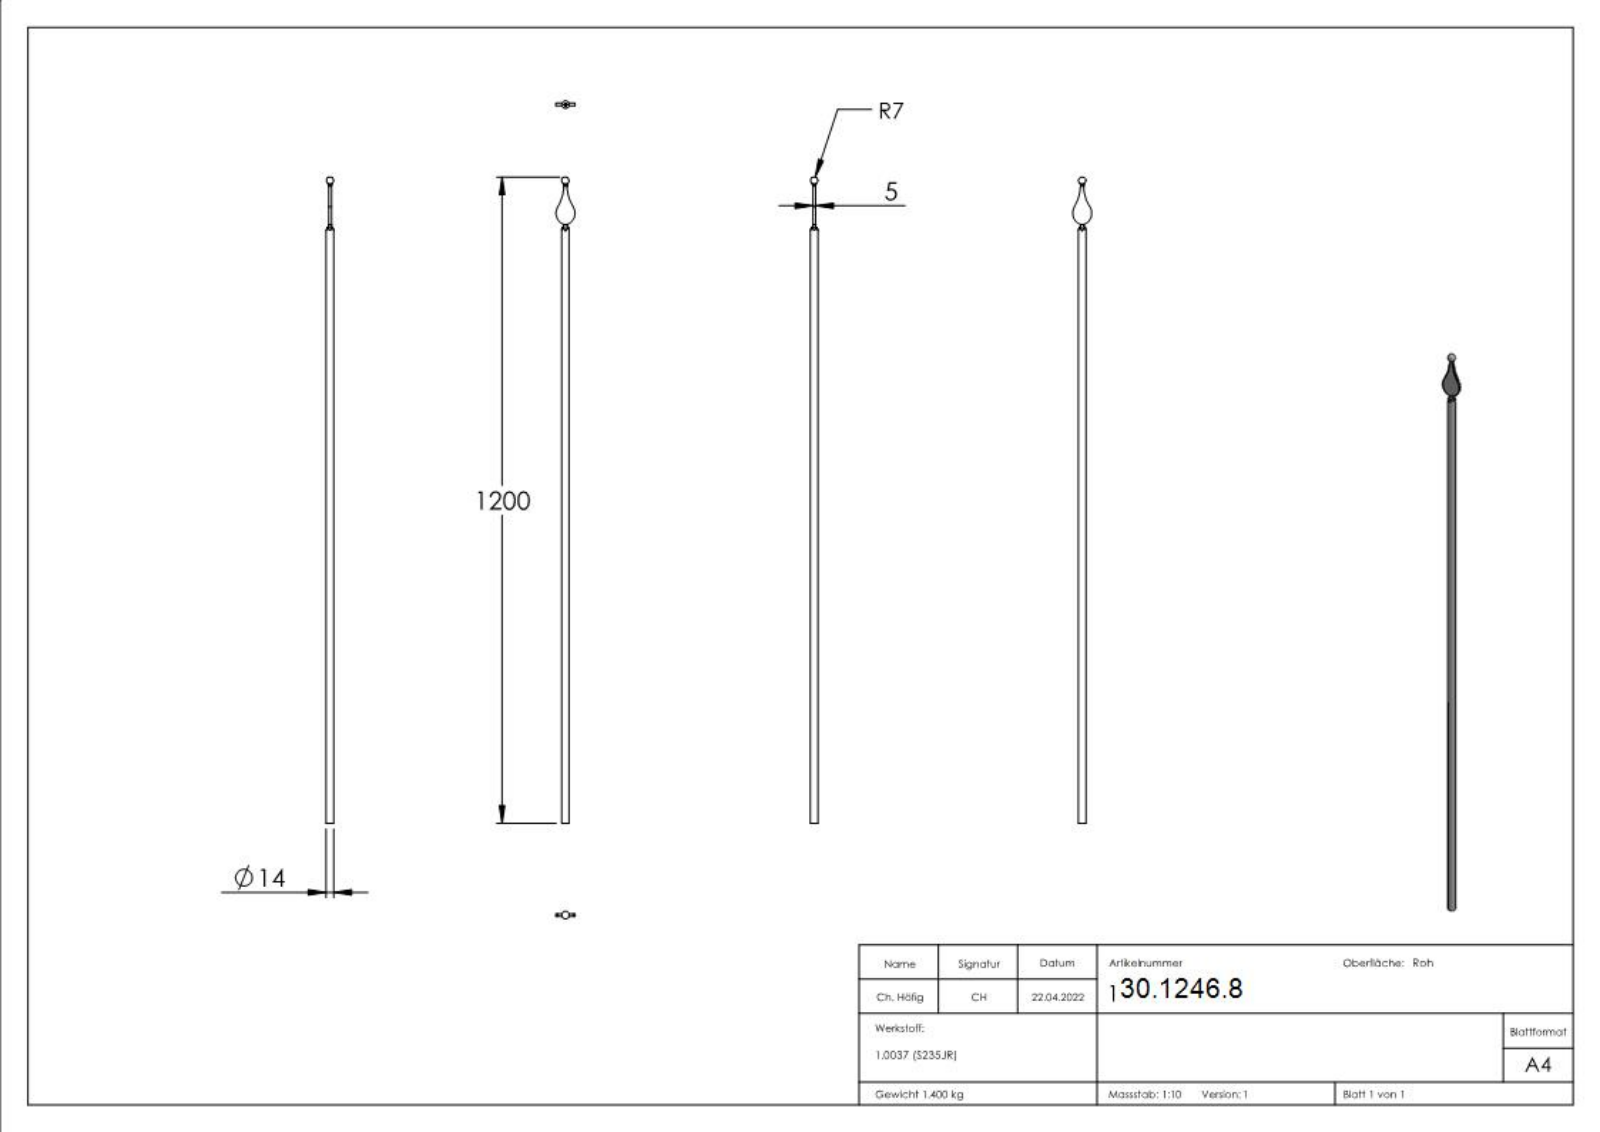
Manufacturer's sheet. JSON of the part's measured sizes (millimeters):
{"part_name": "18517", "step_written_by": "SolidWorks 2018 (CONFIG_CONTROL_DESIGN)", "units": "millimeters", "bodies": {"solids": 1, "faces": 267, "planar": 124, "cylindrical": 15, "other": 128}, "overall_size": [1200, 35, 14], "volume_mm3": 179437, "surface_area_mm2": 53426, "round_bosses_or_shafts": [[14, 1]], "partial_cylinders_radius": [[0.5, 4], [8, 4], [10, 4], [79.94, 2]], "face_to_face_distances": [5, 6, 0.92, 1.76, 2.32, 1.94, 2, 0.83, 3.53, 3.8]}
